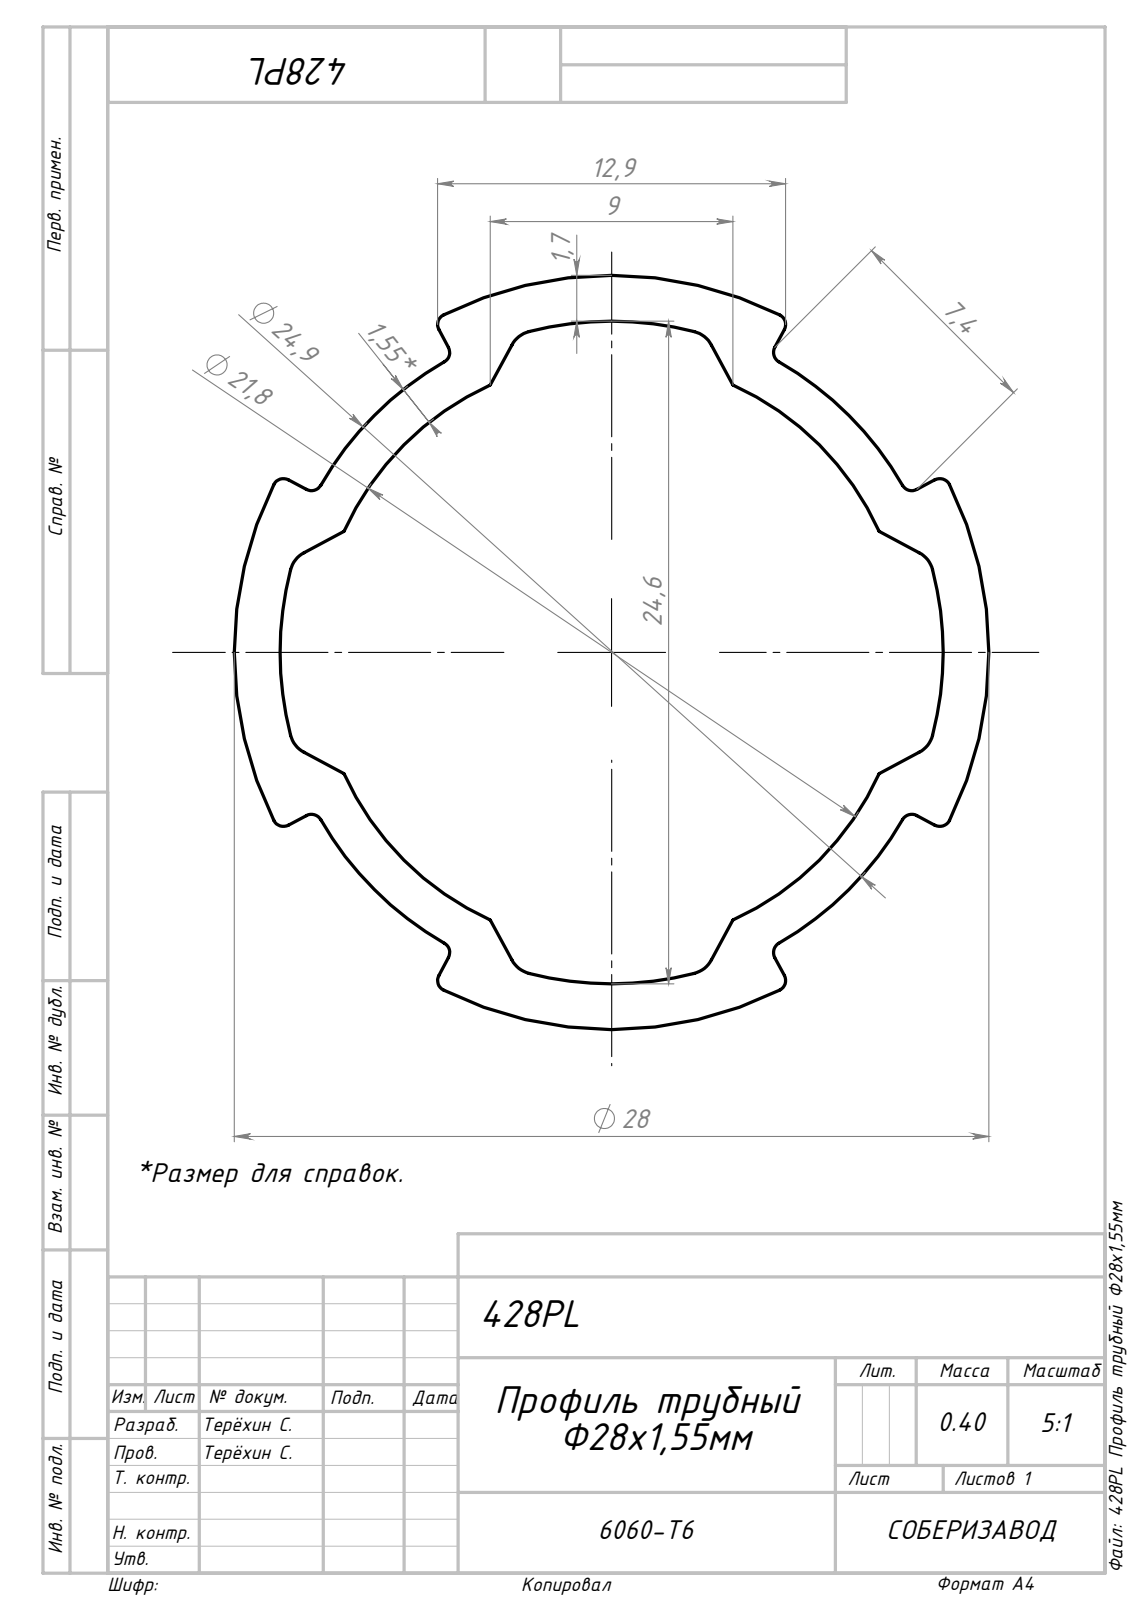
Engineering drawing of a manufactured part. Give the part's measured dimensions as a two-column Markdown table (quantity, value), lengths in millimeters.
| quantity | value |
| --- | --- |
| part name | Сборка2; 428PL Профиль трубный Φ28х1,55мм_00 |
| STEP written by | SolidWorks 2022 (AUTOMOTIVE_DESIGN) |
| units | millimeters |
| bodies | 1 solid, 64 faces (18 planar, 46 cylindrical, 0 other) |
| overall size | 1000 × 28 × 28 |
| volume | 148 751 mm³ |
| surface area | 170 579 mm² |
| partial cylindrical surfaces (radius × count) | 0.4 × 16, 1 × 8, 10.9 × 1, 12.3 × 1, 12.45 × 1, 14 × 1 |
| main face-to-face distances | 17.32, 1000 |
